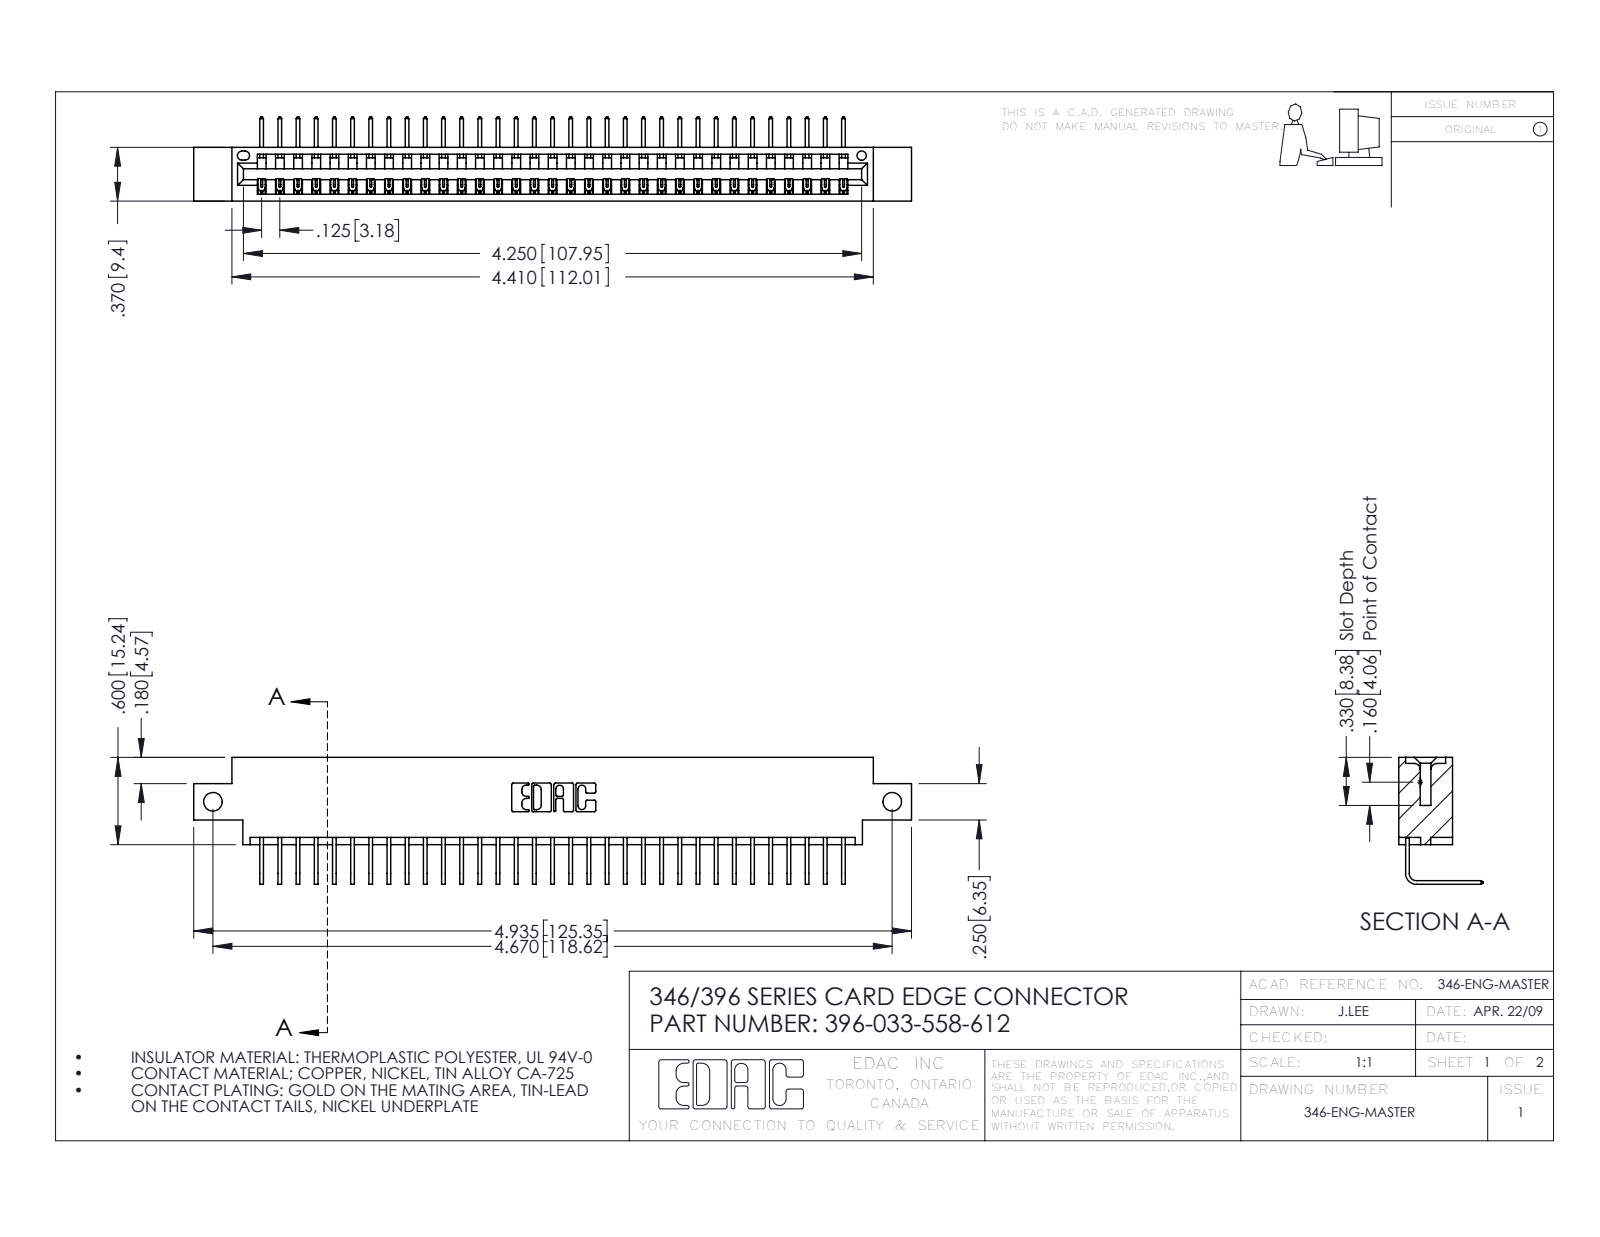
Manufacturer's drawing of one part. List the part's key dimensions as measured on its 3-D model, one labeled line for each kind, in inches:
Part name (STEP PRODUCT): 345-292-001_558 Tail - 2; 396-033-558-612; 346 Part_0.170 Offset - Side Mount
STEP written by: SolidWorks 2016 (CONFIG_CONTROL_DESIGN)
Units: inches
Bodies: 34 solids, 2106 faces (1466 planar, 640 cylindrical, 0 other)
Overall size (bounding box): 4.935 × 0.873 × 0.58
Volume: 0.72 in³ · Surface area: 23.76 in²
Round holes (diameter × count): ⌀0.128 ×2, ⌀0.064 ×1
Partial cylindrical surfaces — rounded edges, fillets, slot ends (radius × count): R0.006 ×66, R0.01 ×22, R0.007 ×6, R0.031 ×6, R0.026 ×3, R0.031 ×2, R0.04 ×2, R0.014 ×1
Main face-to-face distances: 0.322, 0.048, 0.37, 0.25, 0.298, 0.025, 0.072, 0.148, 0.222, 0.1
Hole centre spacings: 4.67
